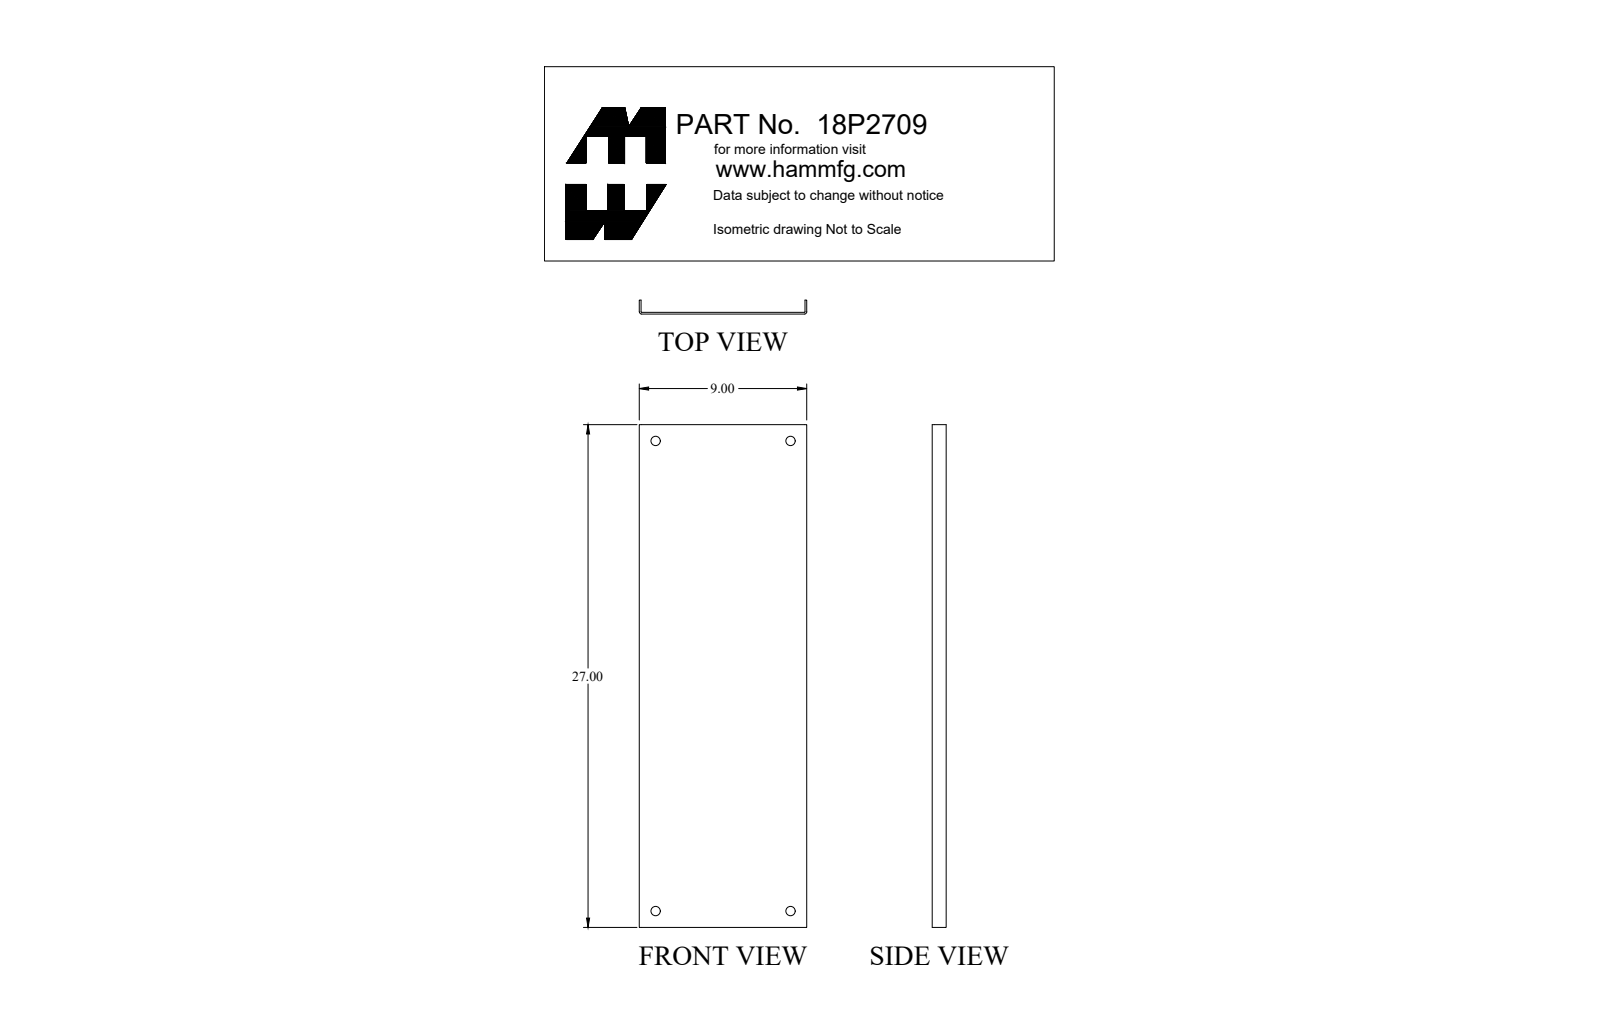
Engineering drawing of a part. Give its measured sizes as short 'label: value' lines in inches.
name: 18P2709_Default
written by: SolidWorks 2018 (CONFIG_CONTROL_DESIGN)
unit: in
bodies: 1 solid, 22 faces (10 planar, 12 cylindrical, 0 other)
size: 27 × 9 × 0.75
volume: 26.2 in³; area: 559.2 in²
holes: 4× ⌀0.5
rounds: 2× R0.03, 2× R0.125
face distances: 0.095, 8.905, 9, 8.81, 0.75, 0.655, 27
hole spacings: 7.25, 25.25, 26.271
